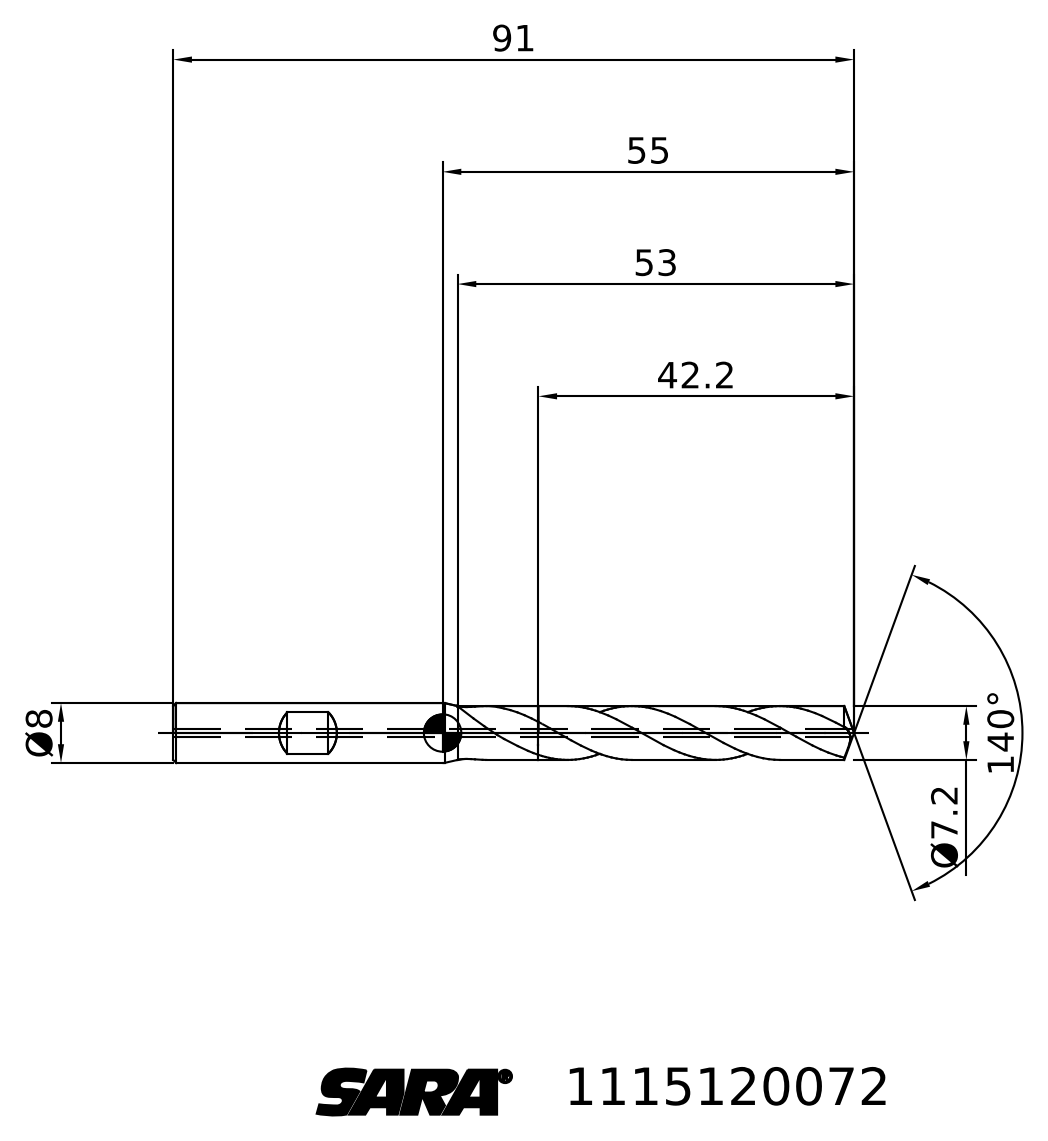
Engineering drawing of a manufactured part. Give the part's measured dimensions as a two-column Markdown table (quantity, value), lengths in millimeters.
| quantity | value |
| --- | --- |
| STEP written by | TDM (AUTOMOTIVE_DESIGN) |
| units | millimeters |
| bodies | 2 solids, 30 faces (6 planar, 0 cylindrical, 24 other) |
| overall size | 91 × 10.3 × 8 |
| volume | 3 295 mm³ |
| surface area | 2 363 mm² |
| main face-to-face distances | 48.8 |
